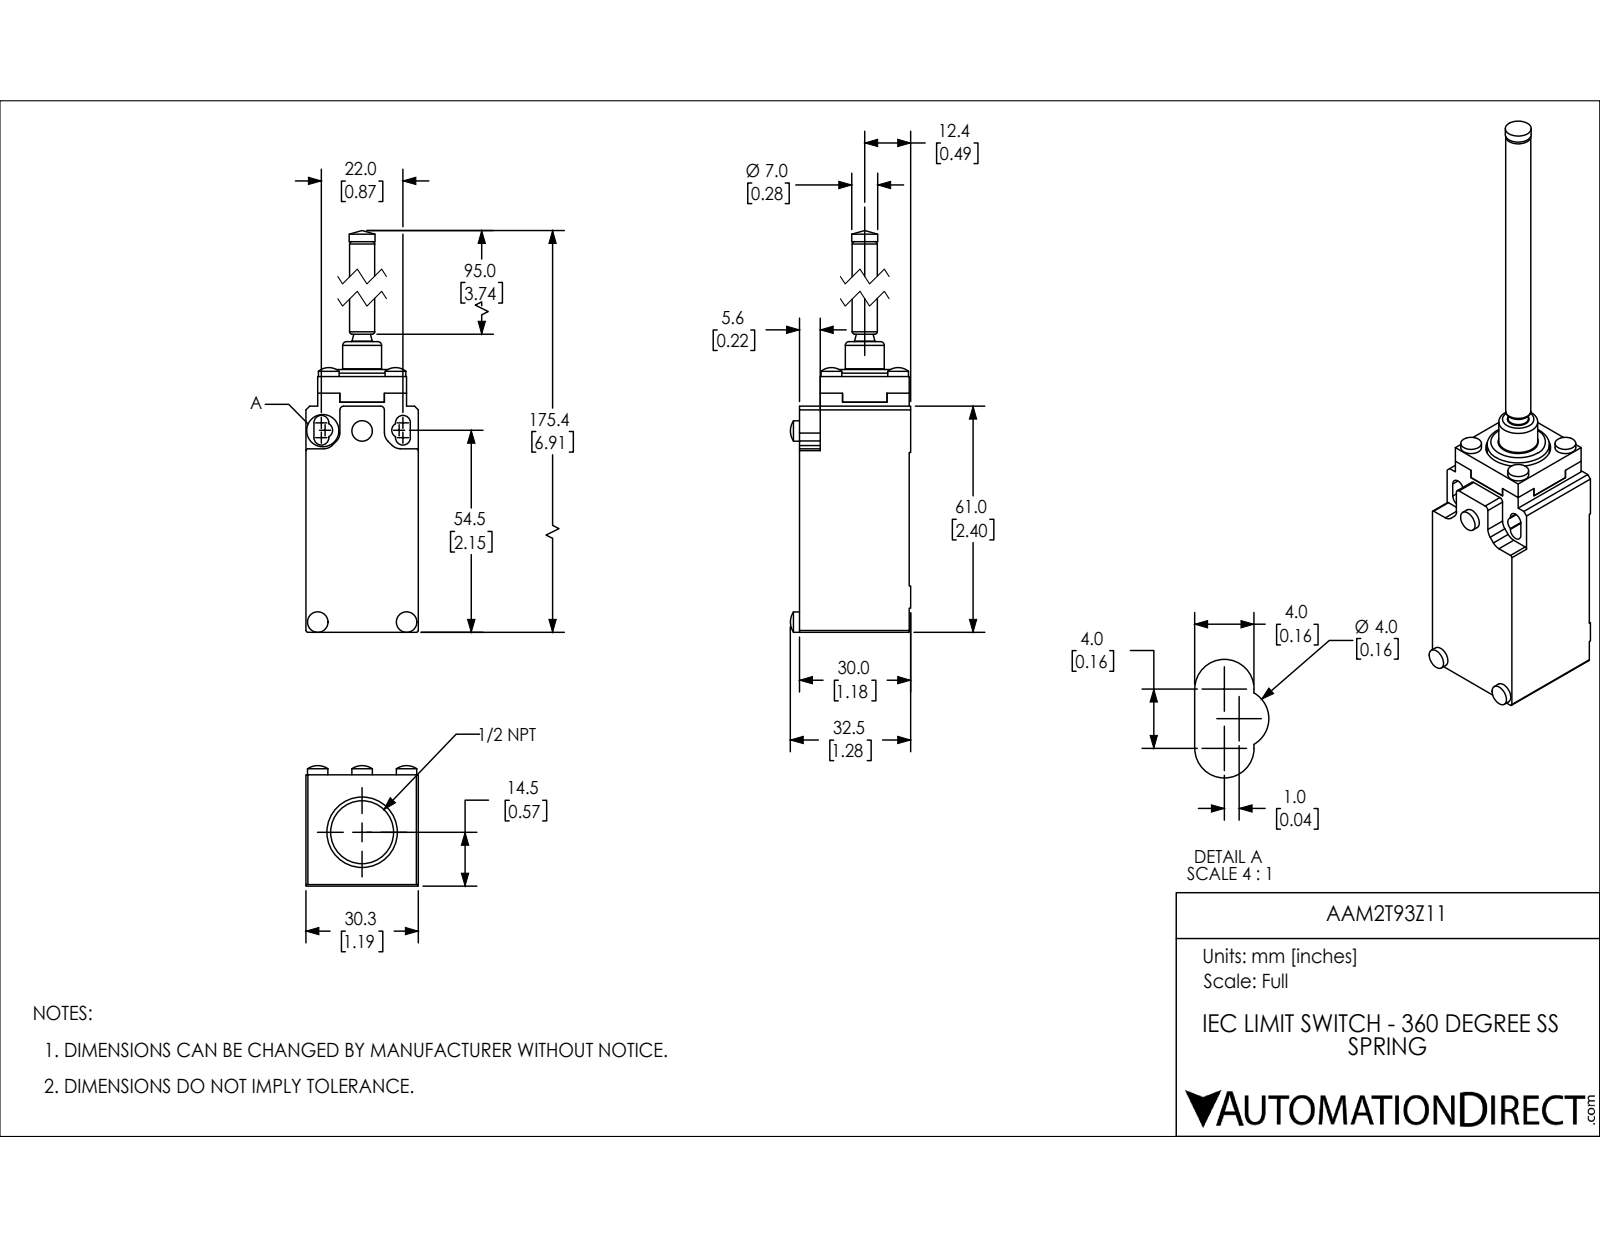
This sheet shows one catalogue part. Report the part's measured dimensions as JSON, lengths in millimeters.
{"part_name": "AAM2T93Z11", "step_written_by": "SolidWorks 2018 (AUTOMOTIVE_DESIGN)", "units": "millimeters", "bodies": {"solids": 3, "faces": 161, "planar": 69, "cylindrical": 63, "other": 29}, "overall_size": [175.4, 32.5, 30.3], "volume_mm3": 60240, "surface_area_mm2": 15230, "round_holes": [[17, 1], [17.5, 1], [19, 1]], "round_bosses_or_shafts": [[5.6, 4], [5.5, 3], [16.8, 1], [10.5, 1], [7, 1], [6.8, 1]], "partial_cylinders_radius": [[2, 6], [0.5, 4], [3, 4], [1, 2], [10, 1], [10.2, 1]], "face_to_face_distances": [30.3, 29.6, 24, 0.4, 30, 6, 62.1, 62.1, 3.1, 27.2], "hole_center_spacings": [2.1]}
